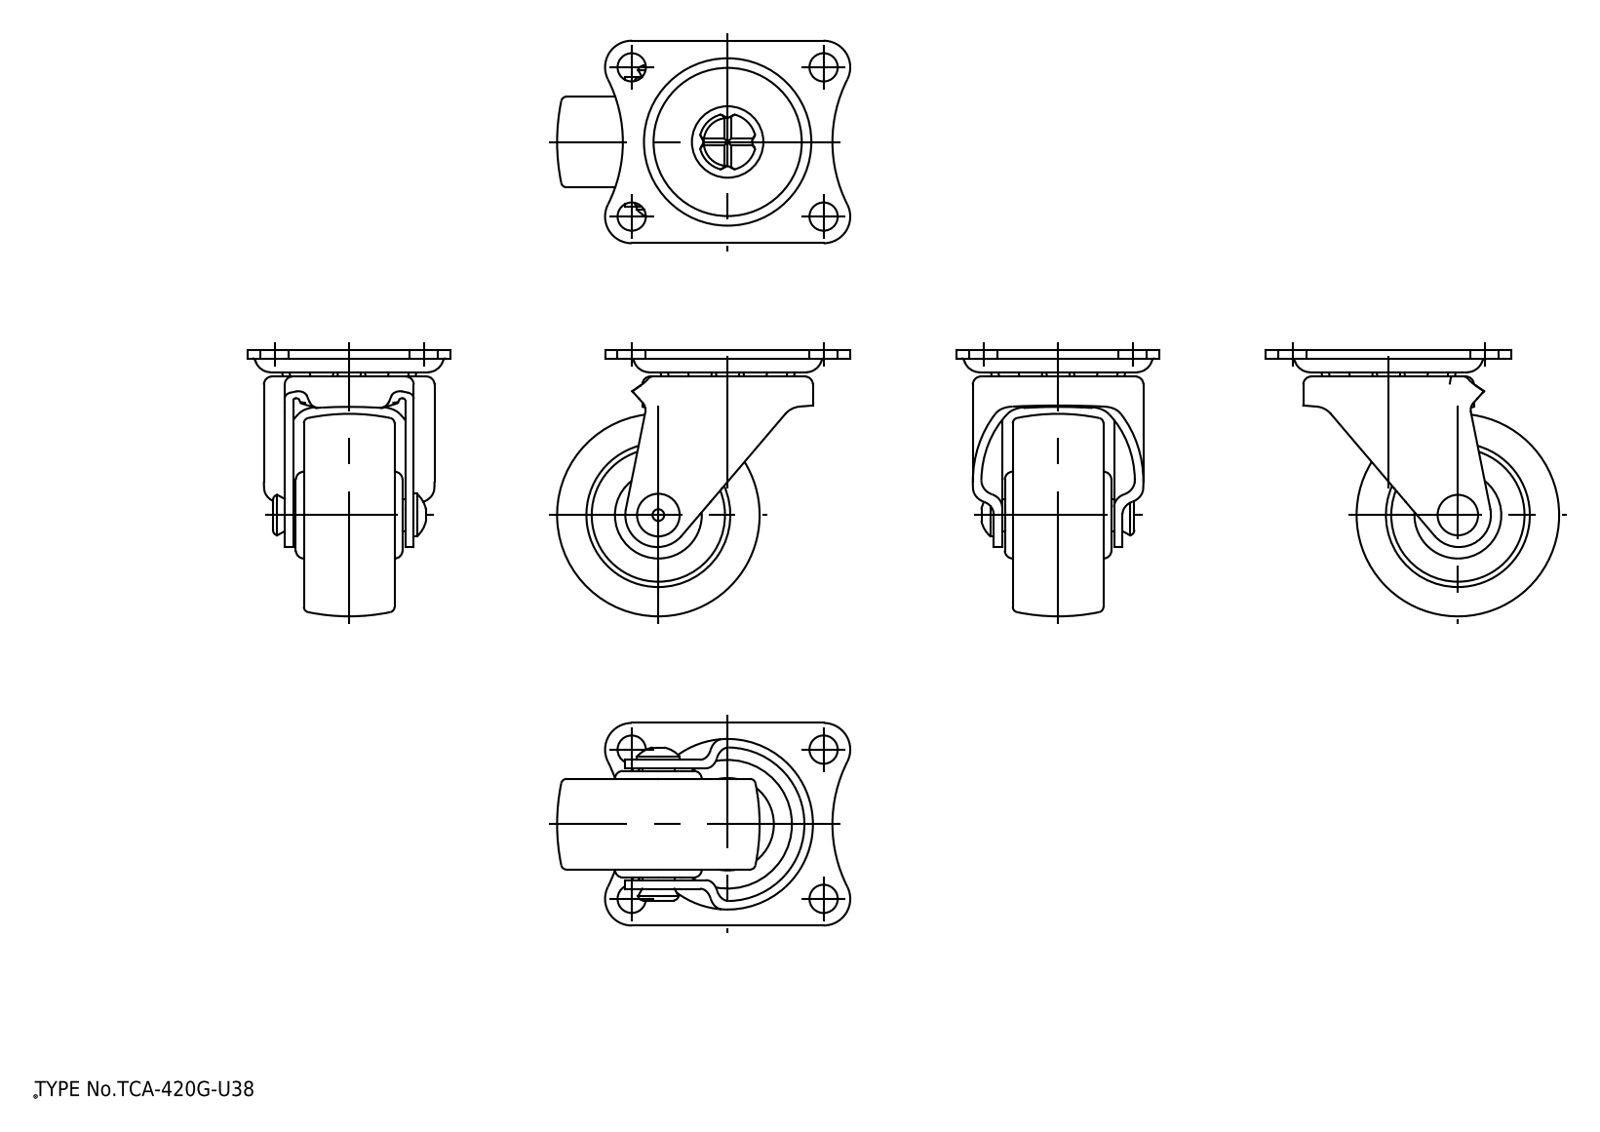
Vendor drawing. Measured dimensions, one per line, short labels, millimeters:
name: wheel; mounting plate; main shaft; axle
written by: spGate 19.8.4 (****-****-****-****) (AUTOMOTIVE_DESIGN)
unit: mm
bodies: 5 solids, 248 faces (66 planar, 72 cylindrical, 110 other)
size: 55 × 50 × 38
volume: 25 811 mm³; area: 14 971 mm²
holes: 4× ⌀5.3, 1× ⌀6.06, 1× ⌀9, 1× ⌀28.8
bosses: 1× ⌀32, 1× ⌀16.29, 1× ⌀12, 1× ⌀8, 1× ⌀6.05
rounds: 8× R0.5, 6× R3, 4× R5, 3× R2, 2× R1, 2× R26, 2× R100, 1× R4
face distances: 1.6, 5, 1, 16, 6.6, 2, 3, 18, 19, 3.4
hole spacings: 22.8, 28, 36, 45.61
